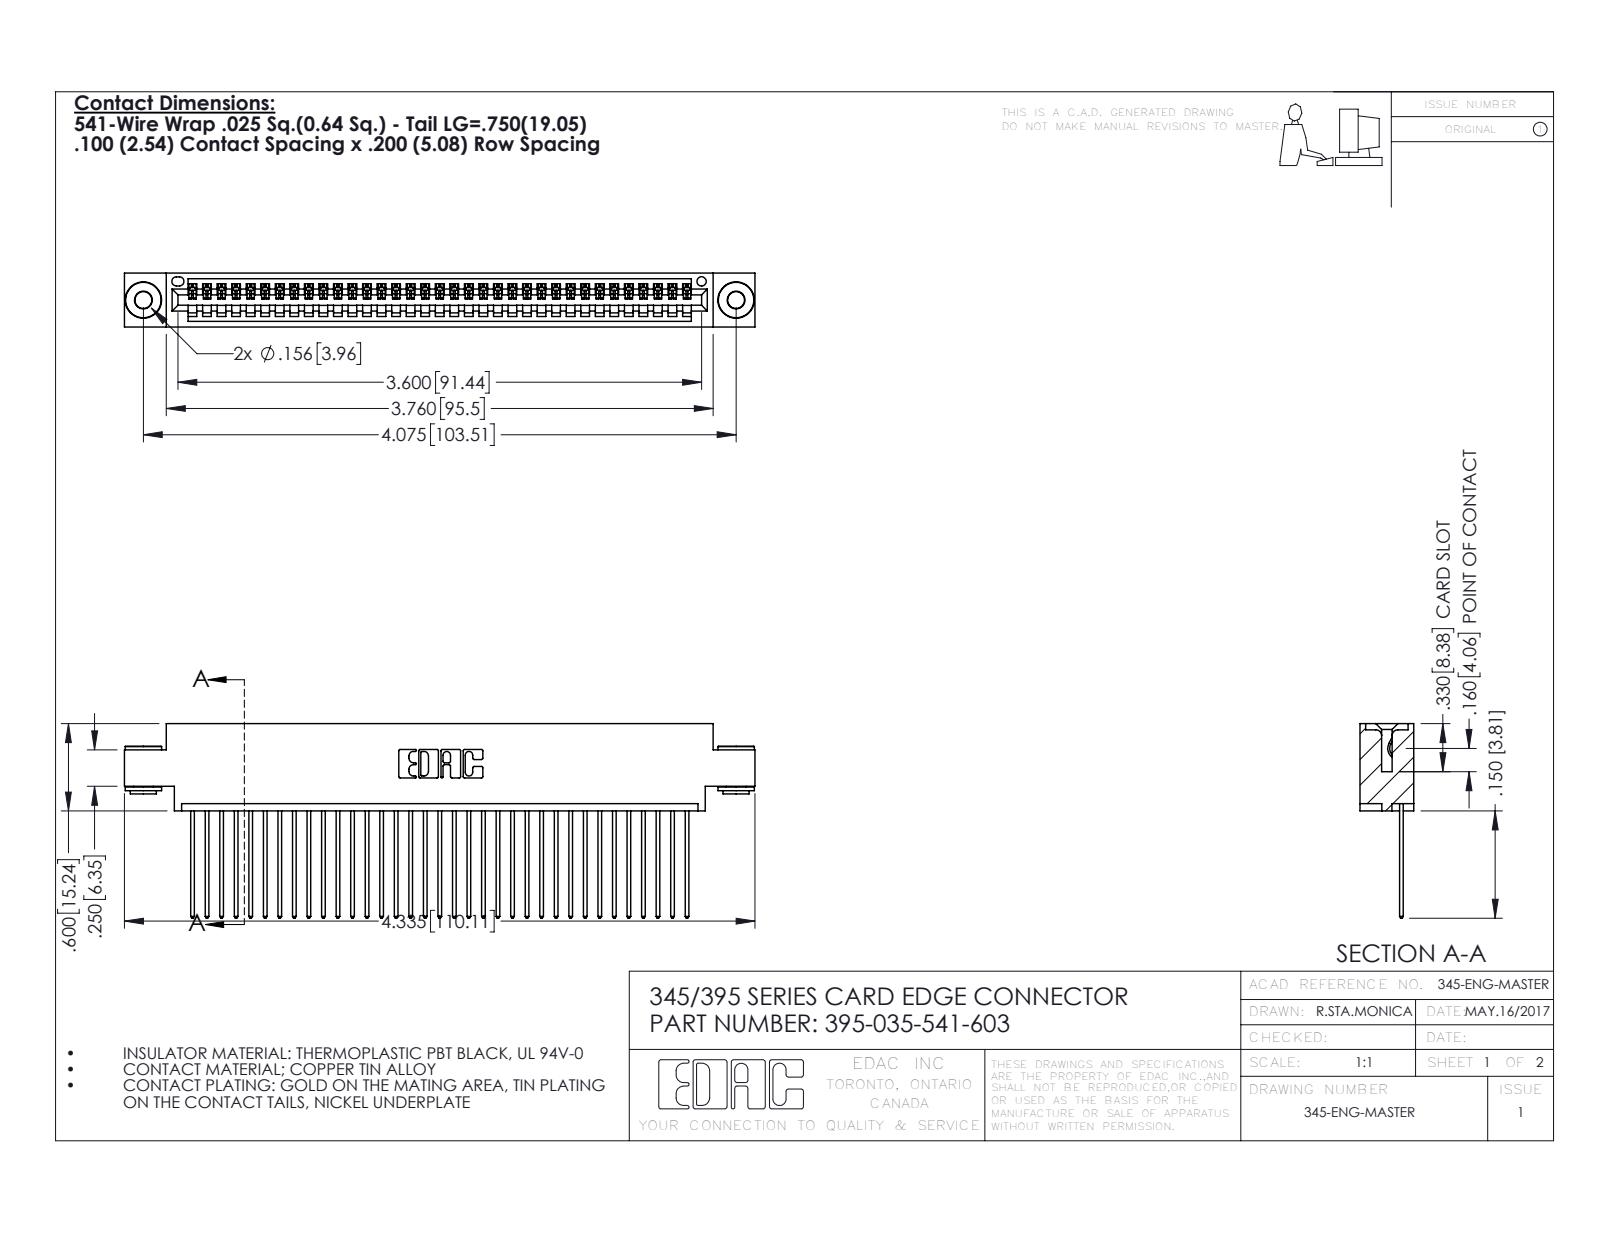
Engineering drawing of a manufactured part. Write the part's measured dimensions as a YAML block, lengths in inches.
part_name: "395-035-541-603; 345-292-001_345-293-141; 345 Part_0.170 Offset - 0.156 Dia-TH; 345-250-002_345-250-002-102"
step_written_by: "SolidWorks 2016 (CONFIG_CONTROL_DESIGN)"
units: inches
bodies: {solids: 38, faces: 2198, planar: 1494, cylindrical: 696, other: 8}
overall_size: [4.335, 1.337, 0.37]
volume: 0.636
surface_area: 22.9
round_holes:
  - {diameter: 0.116, count: 2}
  - {diameter: 0.156, count: 2}
  - {diameter: 0.064, count: 1}
round_bosses_or_shafts:
  - {diameter: 0.25, count: 2}
  - {diameter: 0.18, count: 2}
  - {diameter: 0.136, count: 2}
partial_cylinders:
  - {radius: 0.006, count: 70}
  - {radius: 0.01, count: 70}
  - {radius: 0.01, count: 22}
  - {radius: 0.007, count: 6}
  - {radius: 0.031, count: 6}
  - {radius: 0.026, count: 3}
  - {radius: 0.031, count: 2}
  - {radius: 0.04, count: 2}
face_to_face_distances: [0.072, 0.298, 0.37, 0.098, 0.272, 0.025, 0.2, 0.225, 0.175, 0.149]
hole_center_spacings: [0.27, 3.839, 4.075]
